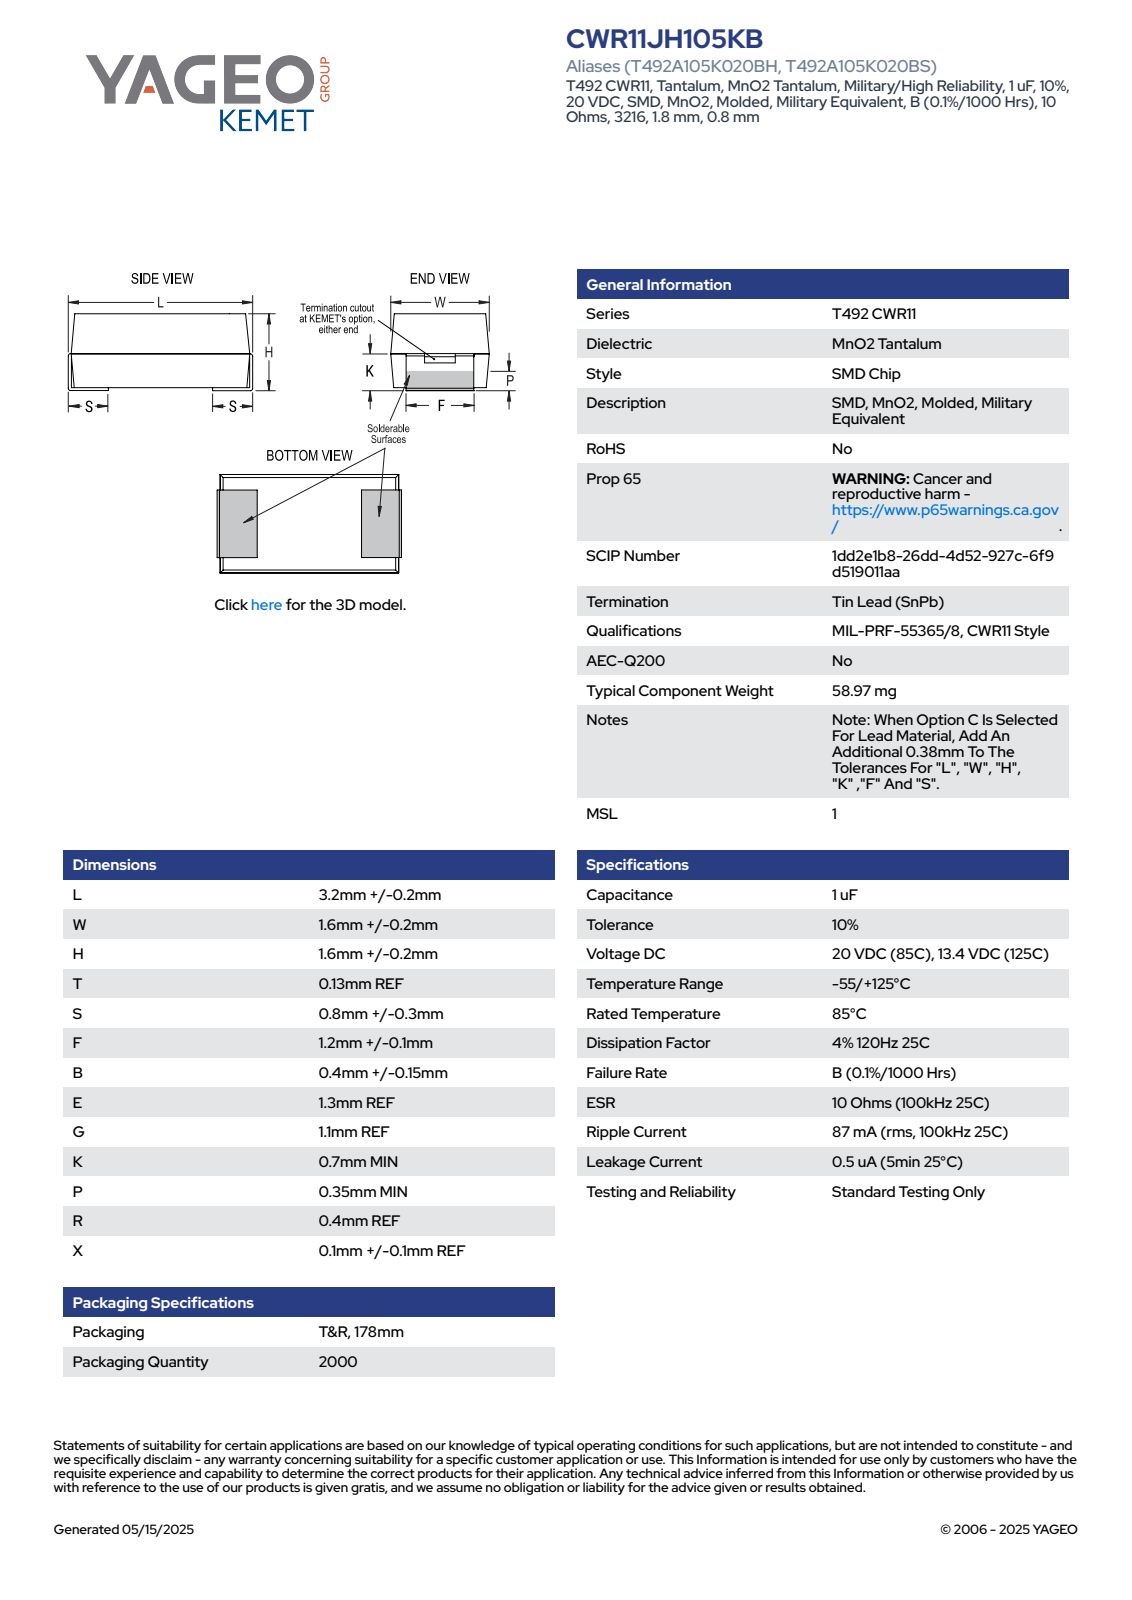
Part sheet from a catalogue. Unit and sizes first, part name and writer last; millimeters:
Units: millimetres
Overall size (bounding box): 3.4 × 1.9 × 1.8
Partial cylindrical surfaces — rounded edges, fillets, slot ends (radius × count): R0.1 ×4
Main face-to-face distances: 1.8, 1.9, 3.3, 3.2, 3.4, 1.3, 0.7, 0.8, 2.6, 2.5
Volume: 10 mm³ · Surface area: 33 mm²
Bodies: 4 solids, 85 faces (81 planar, 4 cylindrical, 0 other)
Part name (STEP PRODUCT): CTS_TCM3M_3216_L3.4H1.8S0.8F1.3K0.7P0.35W1.8
STEP written by: SolidWorks 2014 (AUTOMOTIVE_DESIGN)
